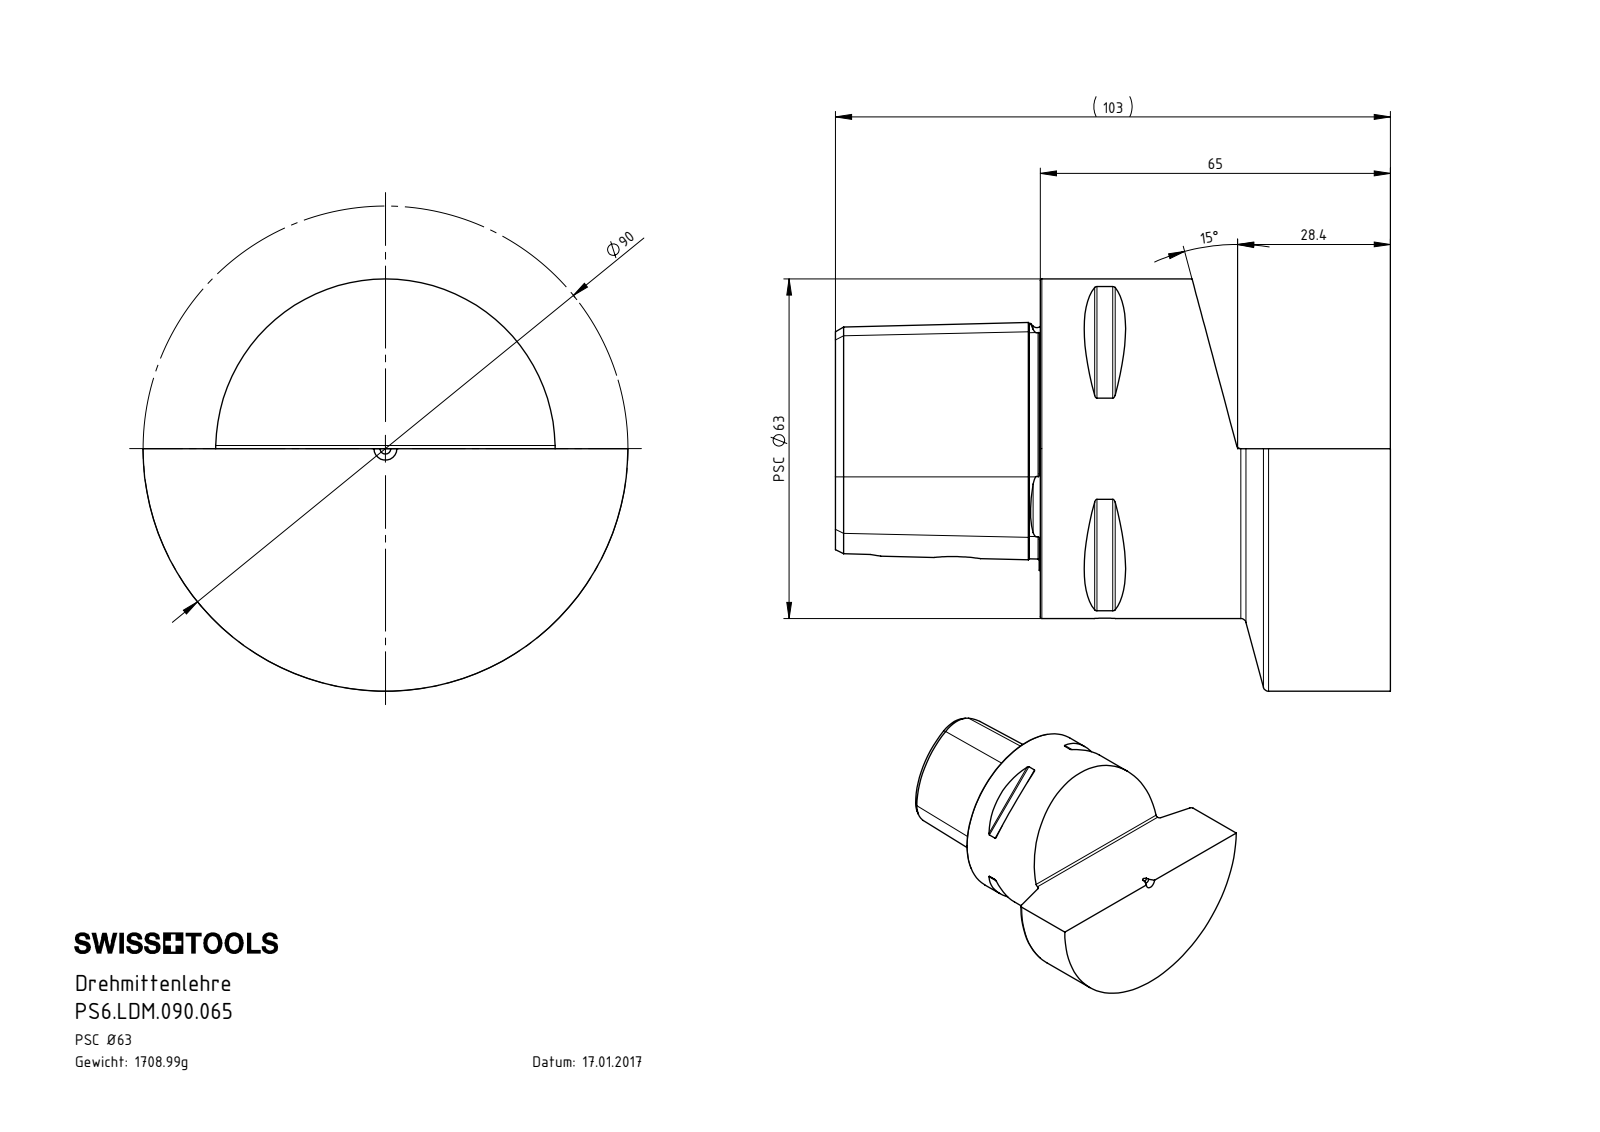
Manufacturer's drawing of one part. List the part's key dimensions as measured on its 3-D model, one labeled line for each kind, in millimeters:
Part name (STEP PRODUCT): PS6-LDM.090.065_A
STEP written by: SolidWorks 2015 (AUTOMOTIVE_DESIGN)
Units: millimetres
Bodies: 1 solid, 125 faces (21 planar, 28 cylindrical, 76 other)
Overall size (bounding box): 103 × 90 × 76.5
Volume: 217 703 mm³ · Surface area: 32 208 mm²
Round holes (diameter × count): ⌀4 ×1, ⌀8.1 ×1, ⌀18 ×1, ⌀28 ×1, ⌀32 ×1
Round bosses / shafts (diameter × count): ⌀63 ×1
Partial cylindrical surfaces — rounded edges, fillets, slot ends (radius × count): R0.5 ×8, R0.8 ×1, R1 ×1, R6 ×1, R45 ×1
Main face-to-face distances: 65, 38, 103, 24.88, 27, 11, 76, 55.8, 37.8, 10.8
Hole centre spacings: 27.5
